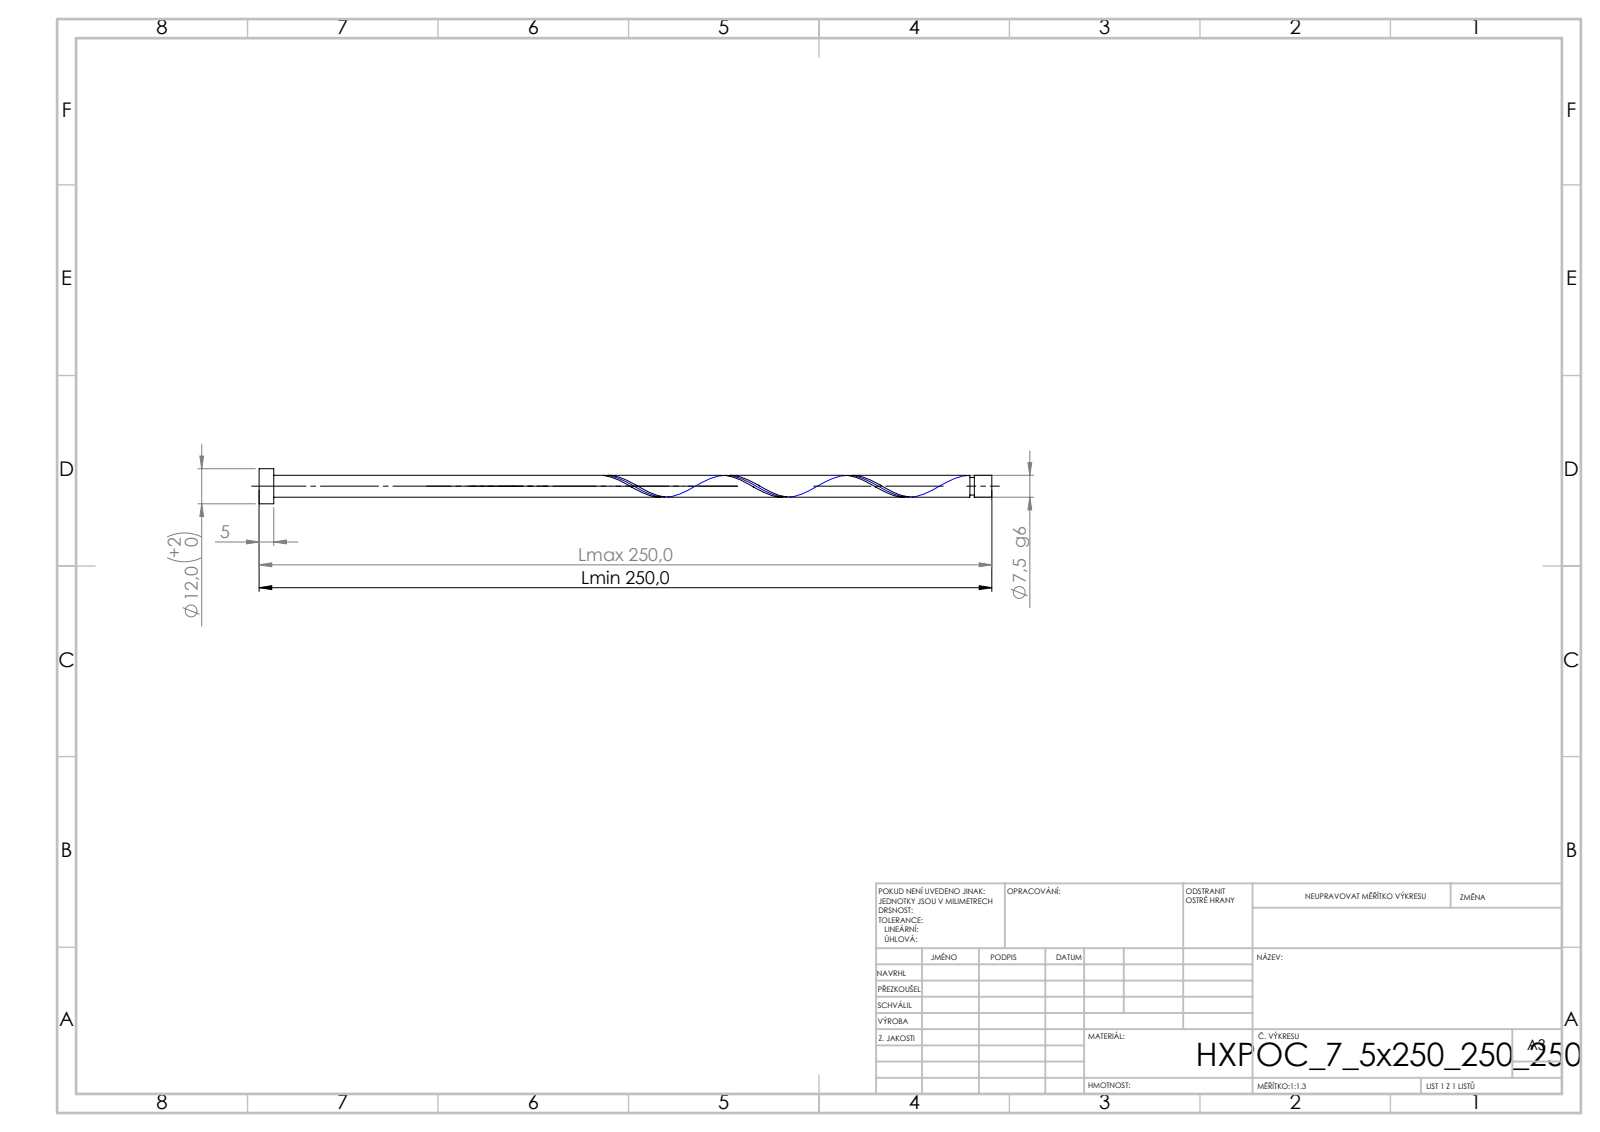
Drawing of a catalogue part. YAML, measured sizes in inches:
step_written_by: "SolidWorks 2019 (CONFIG_CONTROL_DESIGN)"
units: inches
bodies: {solids: 1, faces: 21, planar: 6, cylindrical: 14, other: 1}
overall_size: [9.843, 0.472, 0.472]
volume: 0.687
surface_area: 9.796
round_bosses_or_shafts:
  - {diameter: 0.472, count: 1}
  - {diameter: 0.295, count: 1}
  - {diameter: 0.236, count: 1}
face_to_face_distances: [0.197, 9.843, 9.646, 9.608, 9.411, 0.235, 9.549, 9.352, 0.059, 0.294]
